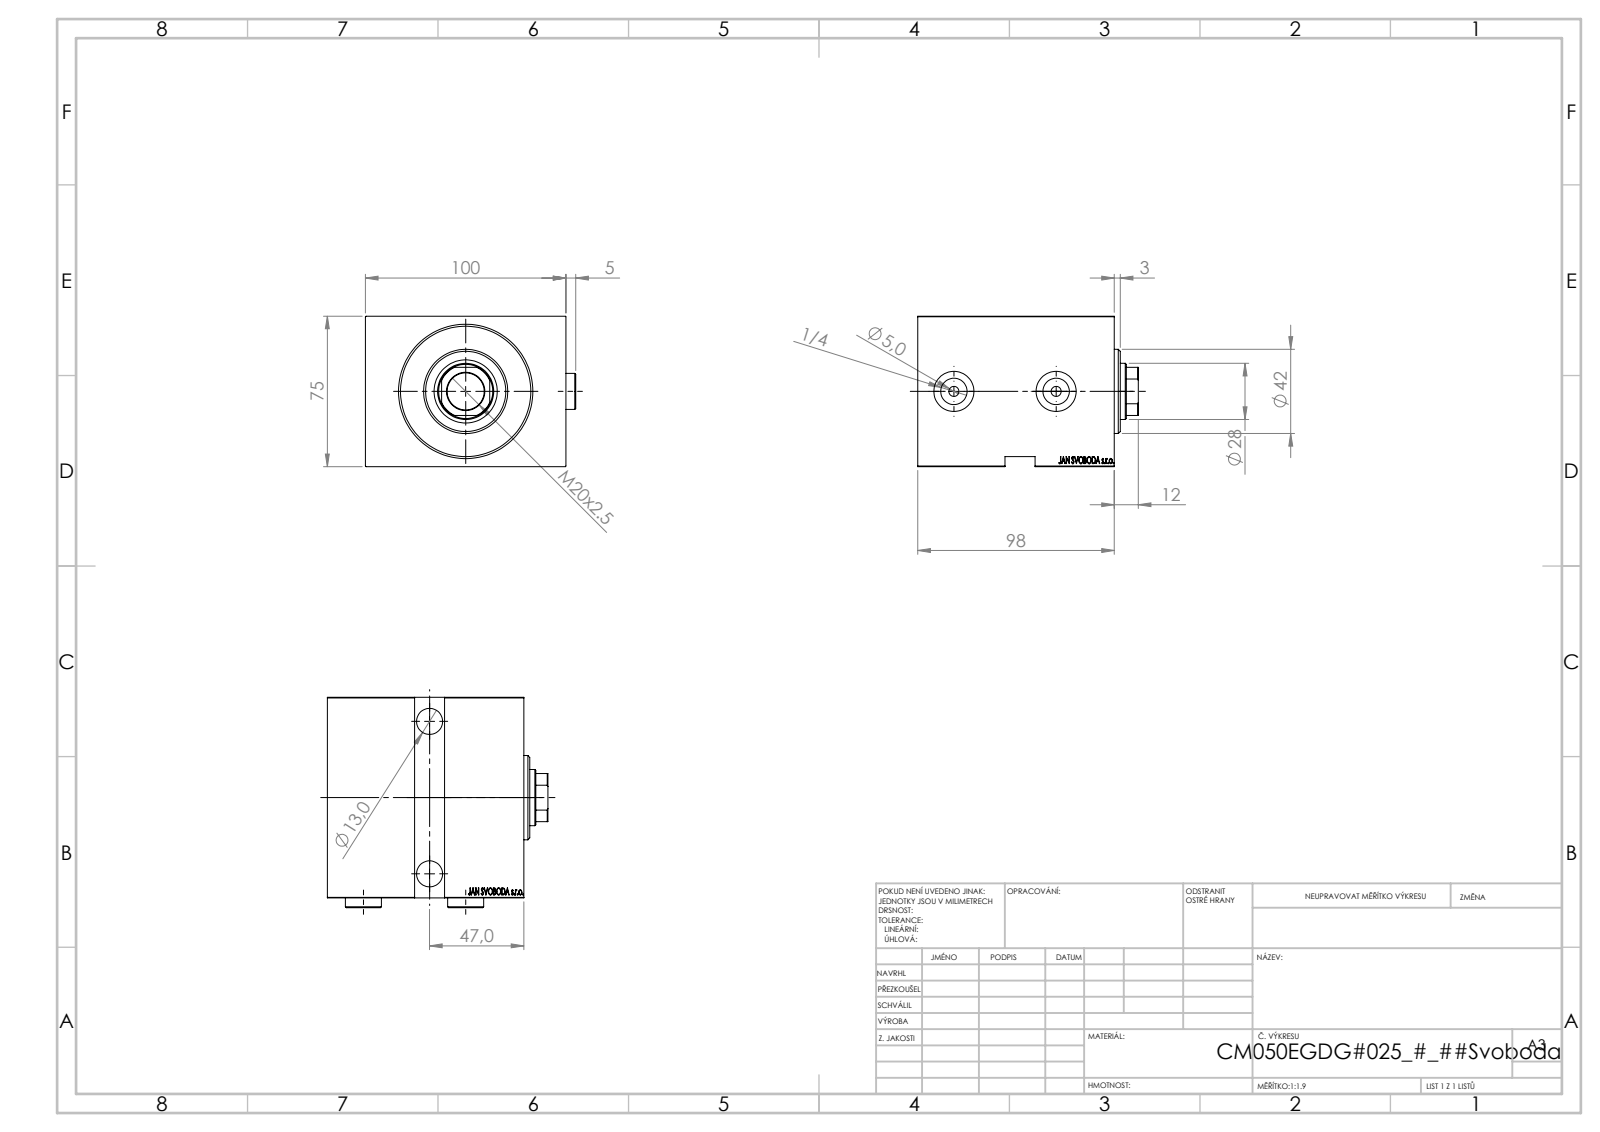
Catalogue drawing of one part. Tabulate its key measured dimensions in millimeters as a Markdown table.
| quantity | value |
| --- | --- |
| part name | V450CM_VC_B; V450CM_E_Body; V450CM_E_VCP; Zatka_OIL_PORT |
| STEP written by | SolidWorks 2019 (CONFIG_CONTROL_DESIGN) |
| units | millimeters |
| bodies | 5 solids, 902 faces (444 planar, 60 cylindrical, 398 other) |
| overall size | 110 × 104.9 × 75 |
| volume | 672 458 mm³ |
| surface area | 101 365 mm² |
| round holes (diameter × count) | 5 × 2, 13 × 2, 13.16 × 2, 19 × 2, 20 × 2, 18.5 × 1, 28 × 1, 31.5 × 1, 50 × 1, 65 × 1 |
| round bosses / shafts (diameter × count) | 18 × 2, 52 × 1, 42 × 1 |
| partial cylindrical surfaces (radius × count) | 13.5 × 1 |
| main face-to-face distances | 75, 100, 98, 5, 14, 84, 79, 93, 81.4, 67.4 |
| hole center spacings | 51, 76 |
